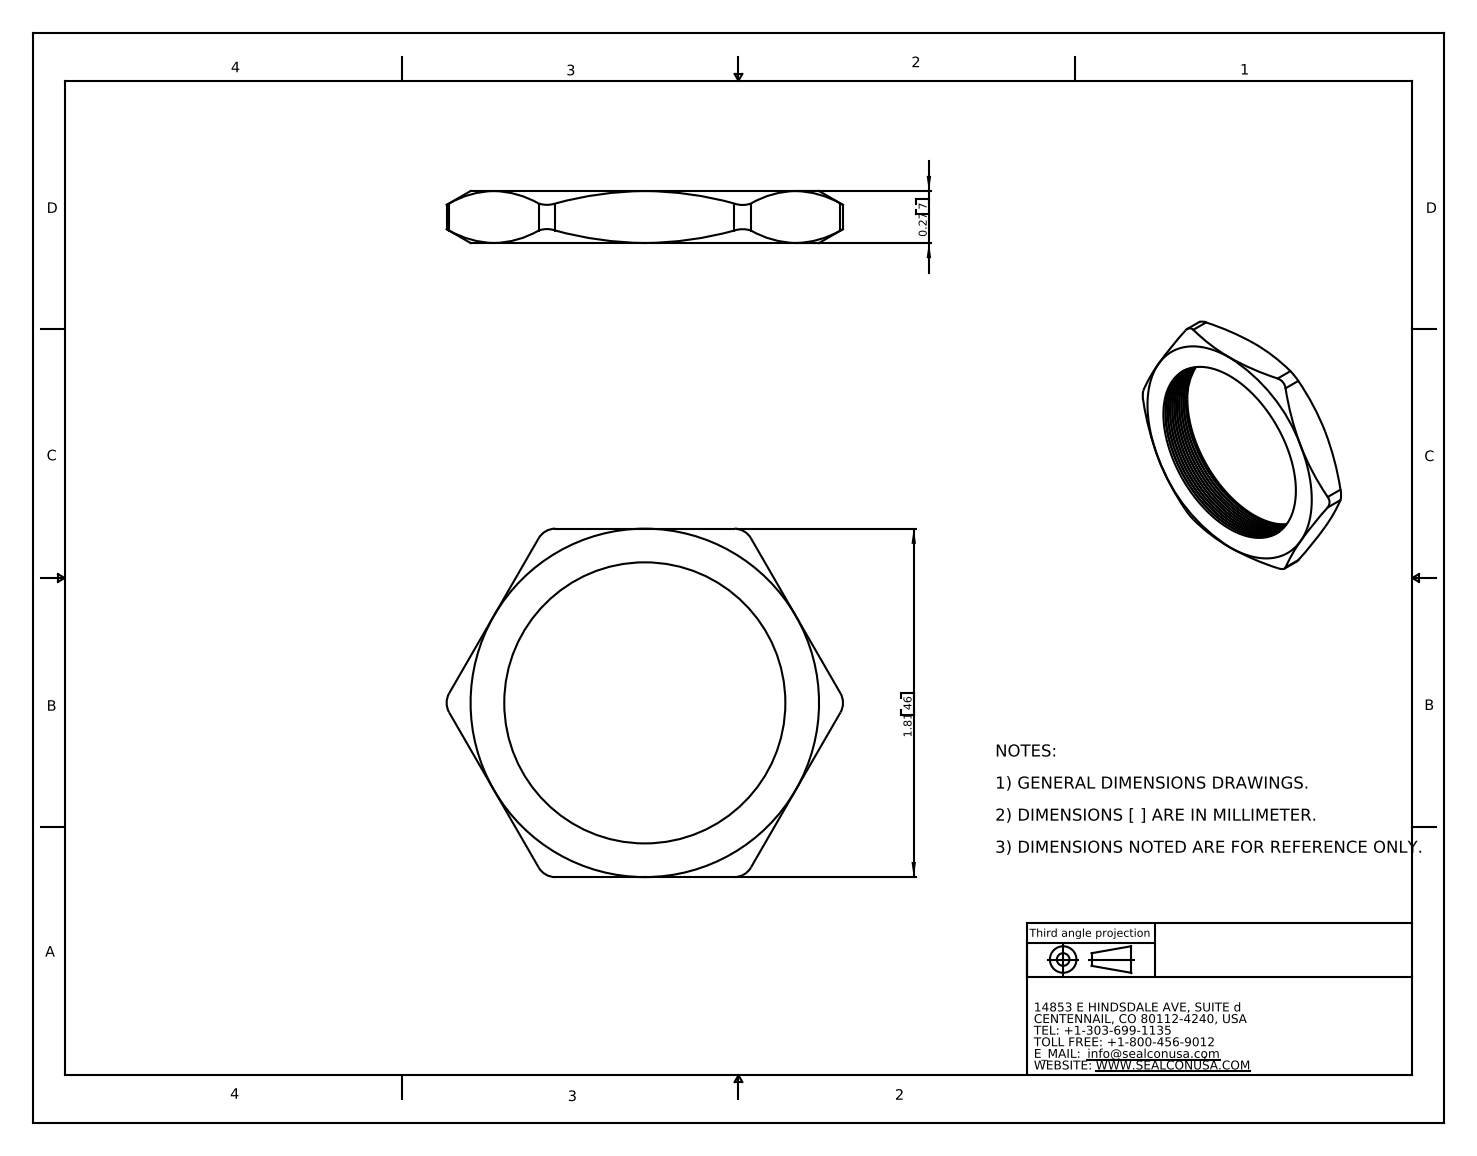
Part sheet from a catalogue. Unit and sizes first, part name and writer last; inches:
Units: inches
Overall size (bounding box): 2.059 × 1.81 × 0.27
Round holes (diameter × count): ⌀1.46 ×1
Partial cylindrical surfaces — rounded edges, fillets, slot ends (radius × count): R0.1 ×6
Main face-to-face distances: 0.27, 1.81
Volume: 0.289 in³ · Surface area: 6.138 in²
Bodies: 1 solid, 93 faces (8 planar, 27 cylindrical, 58 other)
Part name (STEP PRODUCT): NP-29
STEP written by: SolidWorks 2007 (CONFIG_CONTROL_DESIGN)
